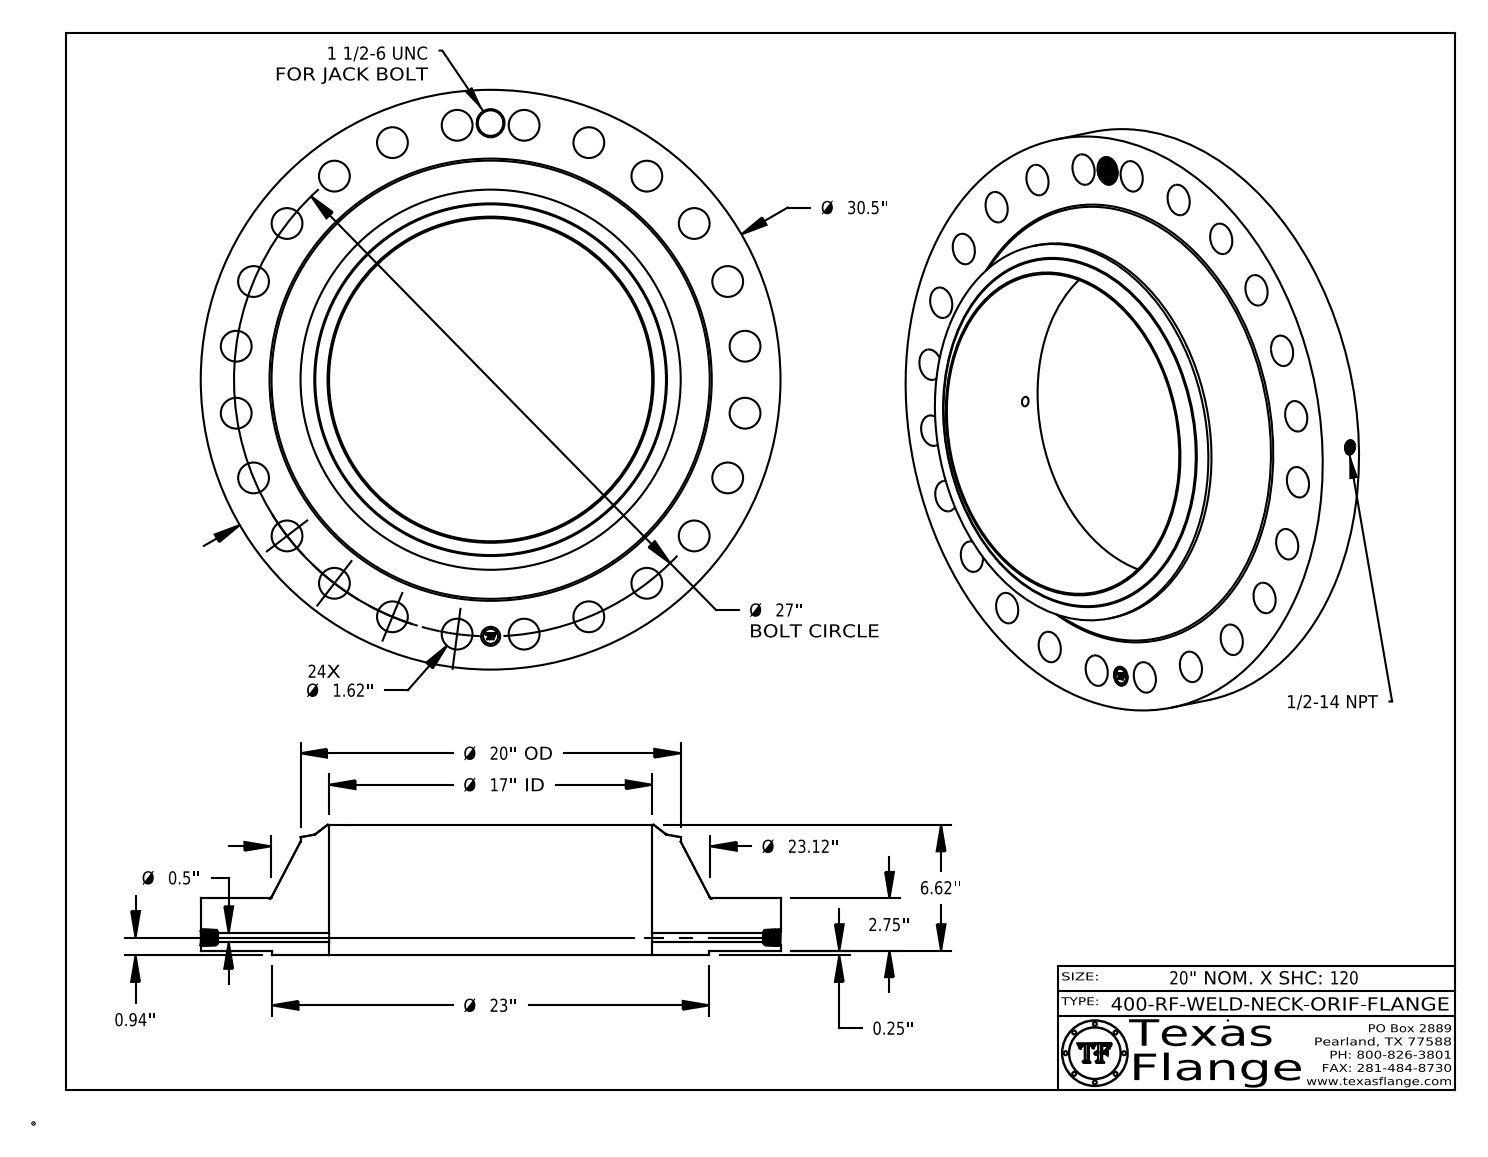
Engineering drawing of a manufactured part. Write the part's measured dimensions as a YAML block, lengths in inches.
part_name: "400-RF-WELD-NECK"
step_written_by: "CATIA V5 STEP AP214 (AUTOMOTIVE_DESIGN)"
units: inches
bodies: {solids: 1, faces: 814, planar: 369, cylindrical: 129, other: 316}
overall_size: [30.5, 30.5, 6.87]
volume: 1744
surface_area: 2078
round_holes:
  - {diameter: 1.62, count: 24}
  - {diameter: 0.5, count: 1}
  - {diameter: 0.672, count: 1}
  - {diameter: 1, count: 1}
  - {diameter: 1.344, count: 1}
  - {diameter: 17, count: 1}
round_bosses_or_shafts:
  - {diameter: 0.061, count: 8}
  - {diameter: 30.5, count: 1}
  - {diameter: 23, count: 1}
  - {diameter: 20, count: 1}
  - {diameter: 0.788, count: 1}
face_to_face_distances: [2.75, 0.25, 3, 6.87, 6.62, 3.87, 2.985, 2.735, 0.015, 3.885]
hole_center_spacings: [13.5, 23.383, 24.945, 21.42, 3.524, 6.988, 19.092, 26.08]
